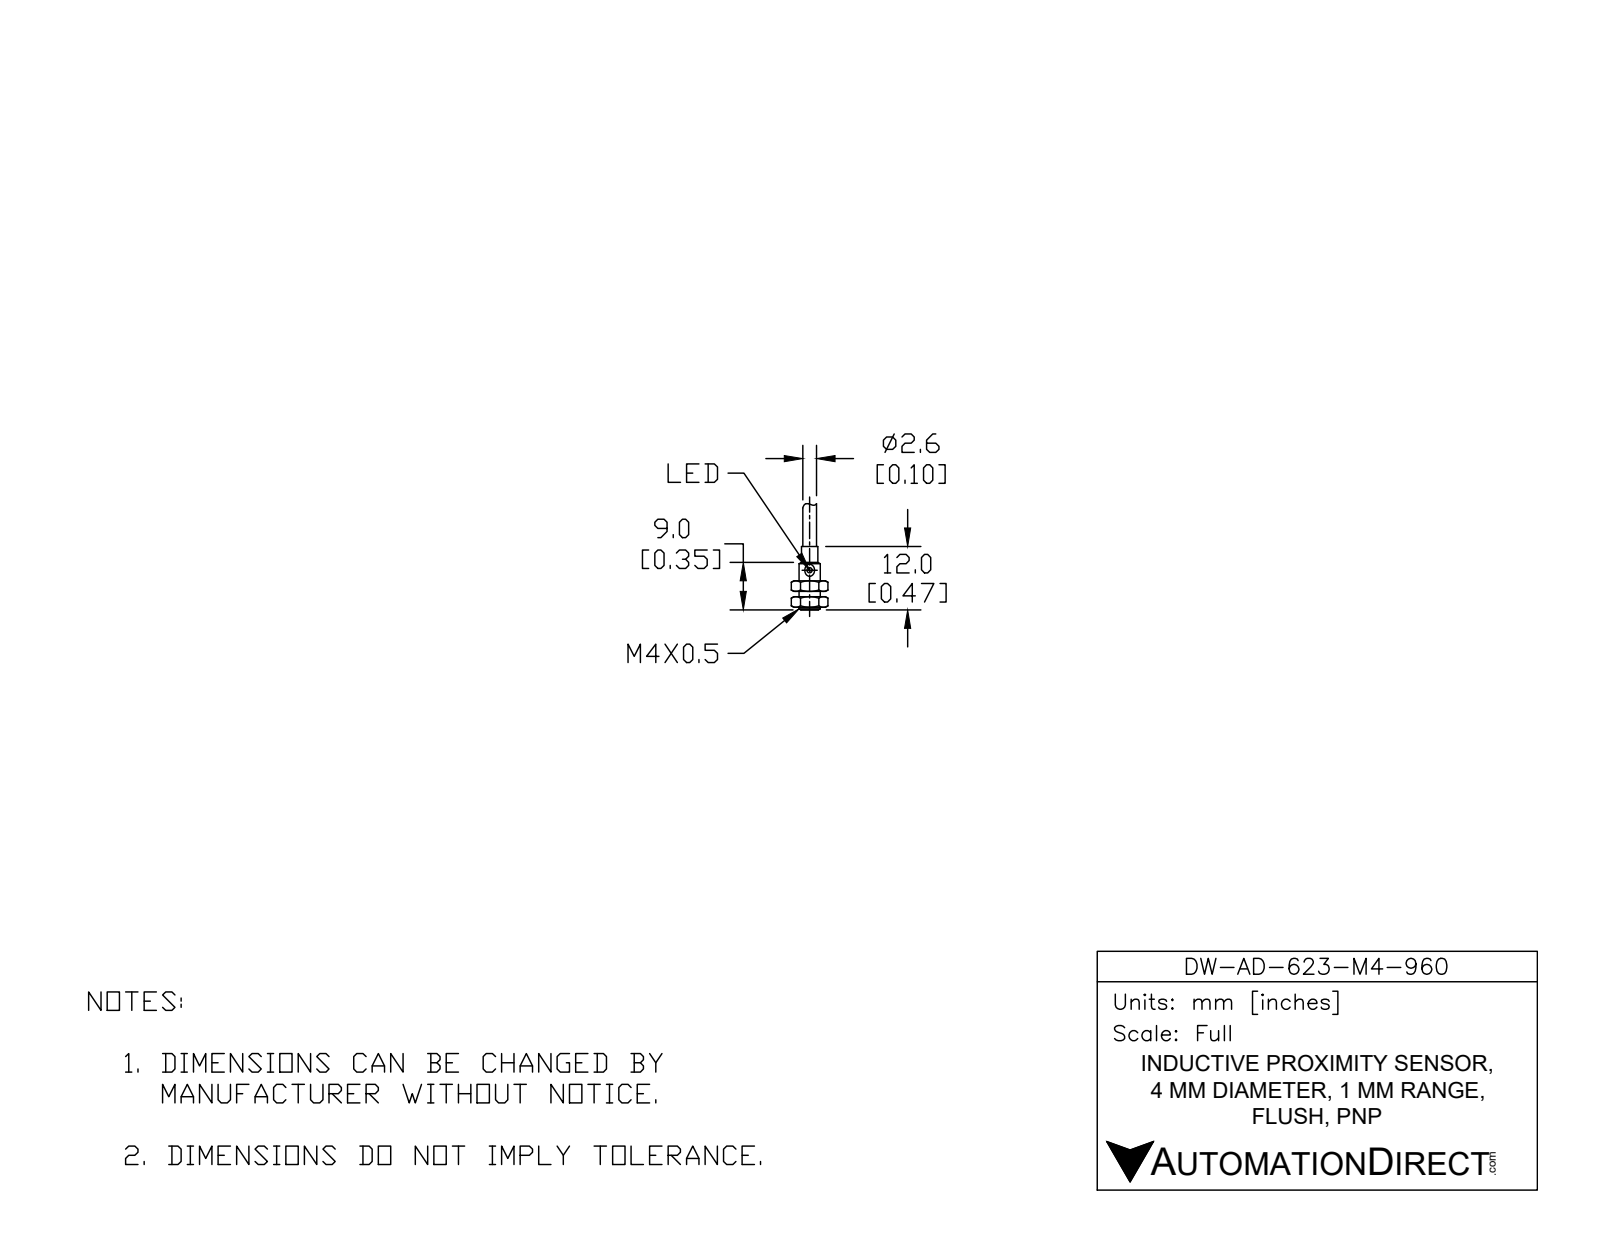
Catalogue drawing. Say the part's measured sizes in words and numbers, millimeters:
The part is named "DW-AD-623-M4-960". Its 3-D file was written by "SolidWorks 2017 (AUTOMOTIVE_DESIGN)". It is 2 solids with 14 faces: 6 planar, 3 cylindrical and 5 other. Overall it measures 19.1 by 4 by 4 millimeters. Its volume is 230 cubic millimeters and its surface area 328 square millimeters. Round bosses or shafts: 1 of diameter 4, 1 of diameter 3.1, 1 of diameter 2.6. The main face-to-face distances are 12, 11.9.
